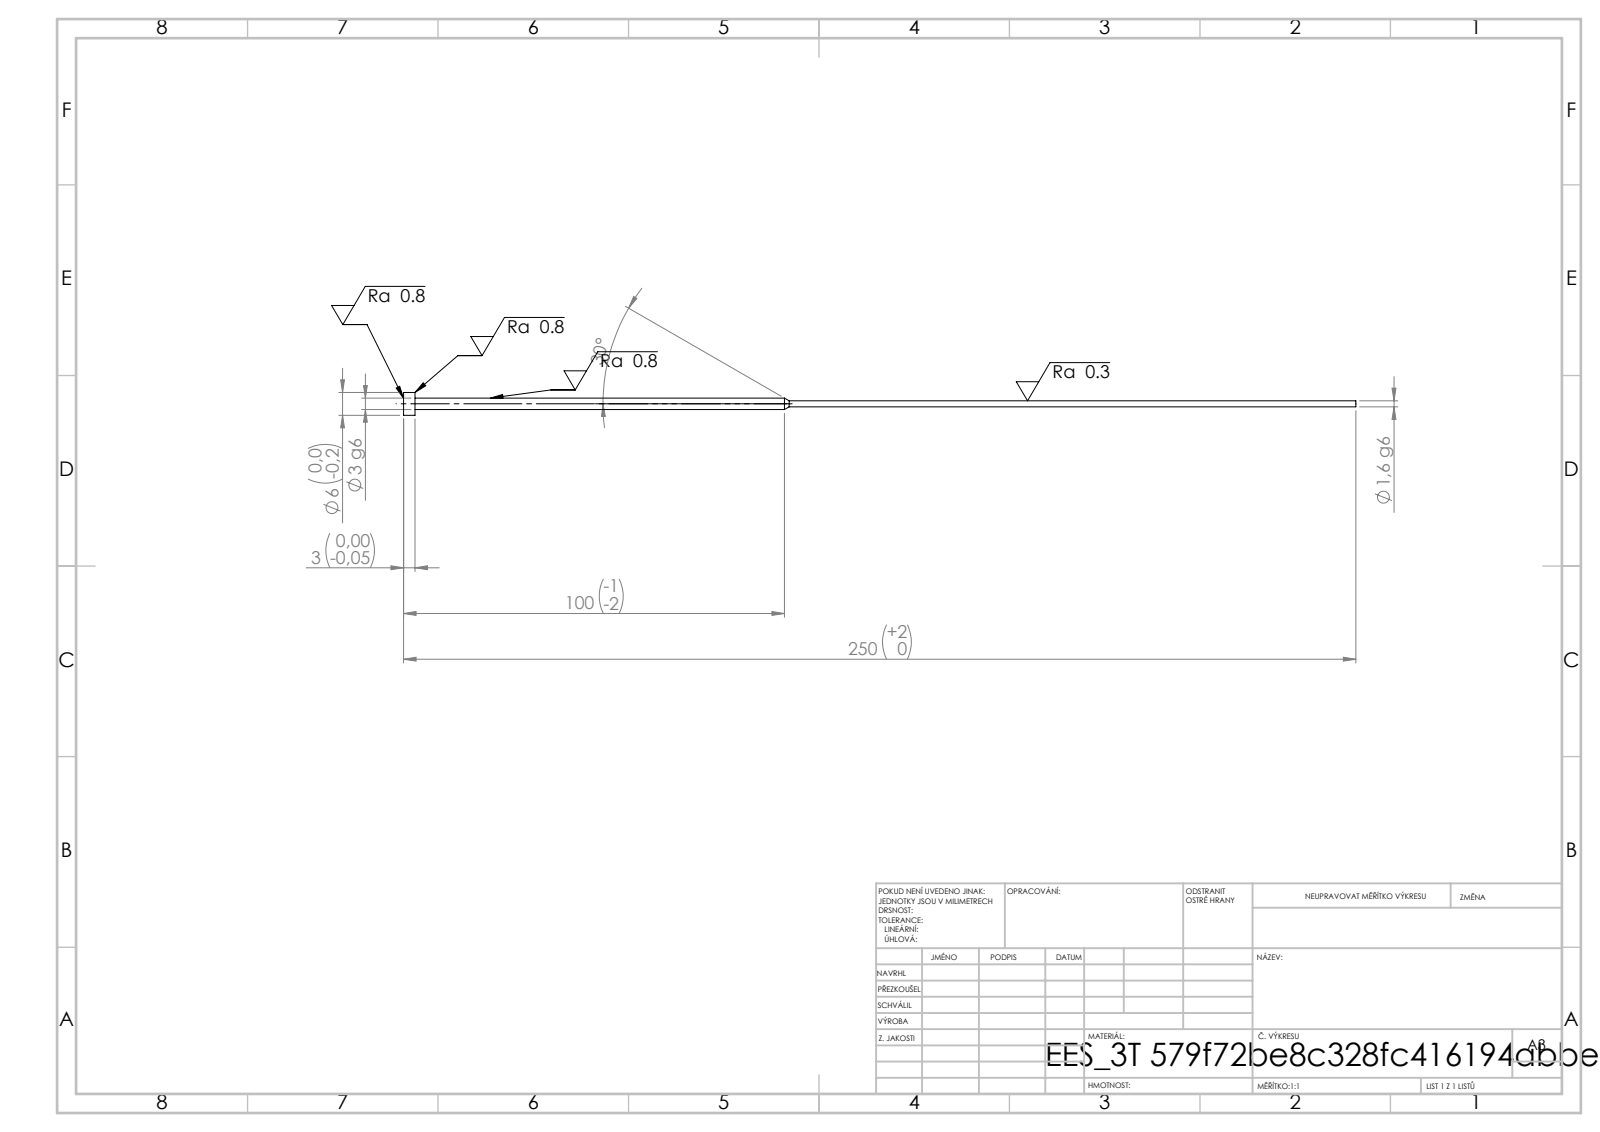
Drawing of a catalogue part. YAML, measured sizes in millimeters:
step_written_by: "SolidWorks 2019 (CONFIG_CONTROL_DESIGN)"
units: millimeters
bodies: {solids: 1, faces: 11, planar: 3, cylindrical: 6, other: 2}
overall_size: [250, 6, 6]
volume: 1075
surface_area: 1780
round_bosses_or_shafts:
  - {diameter: 6, count: 1}
  - {diameter: 3, count: 1}
  - {diameter: 1.6, count: 1}
face_to_face_distances: [3, 247, 250]
